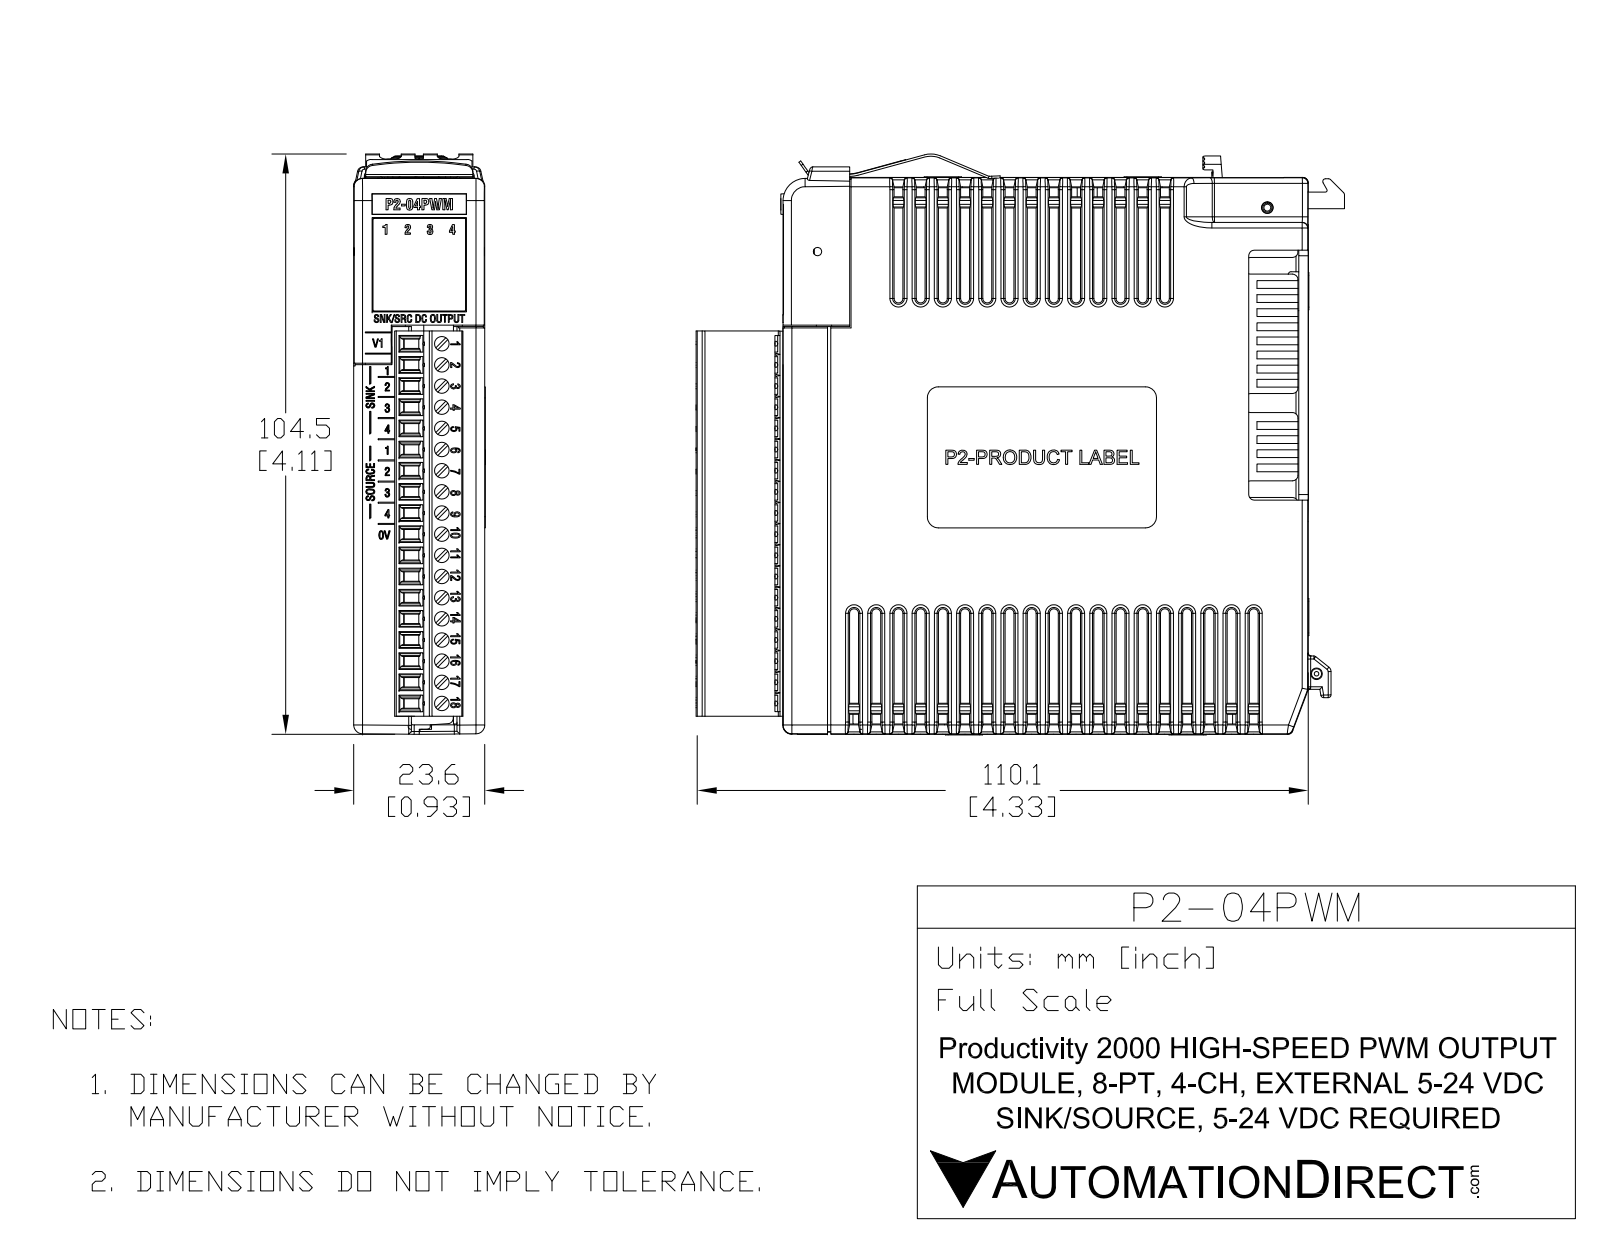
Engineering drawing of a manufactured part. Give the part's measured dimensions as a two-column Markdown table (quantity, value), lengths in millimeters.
| quantity | value |
| --- | --- |
| part name | P2-04PWM Red 1 v18 r3 v17 Coord Ext Combi 2 fXT r1 EXT2 |
| STEP written by | SolidWorks 2017 (AUTOMOTIVE_DESIGN) |
| units | millimeters |
| bodies | 2 solids, 2861 faces (1877 planar, 489 cylindrical, 495 other) |
| overall size | 104.6 × 101.8 × 24.4 |
| volume | 208 000 mm³ |
| surface area | 41 940 mm² |
| round holes (diameter × count) | 1.2 × 2, 1.5 × 1 |
| partial cylindrical surfaces (radius × count) | 0.5 × 148, 0.2 × 80, 1 × 70, 1.5 × 20, 1.6 × 18, 1.6 × 13, 0.3 × 9, 1.7 × 4 |
| main face-to-face distances | 23.6, 11, 6.9, 4.1, 12.6, 19.6, 15.2, 4, 2.4, 3.8 |
| hole center spacings | 15.7 |
